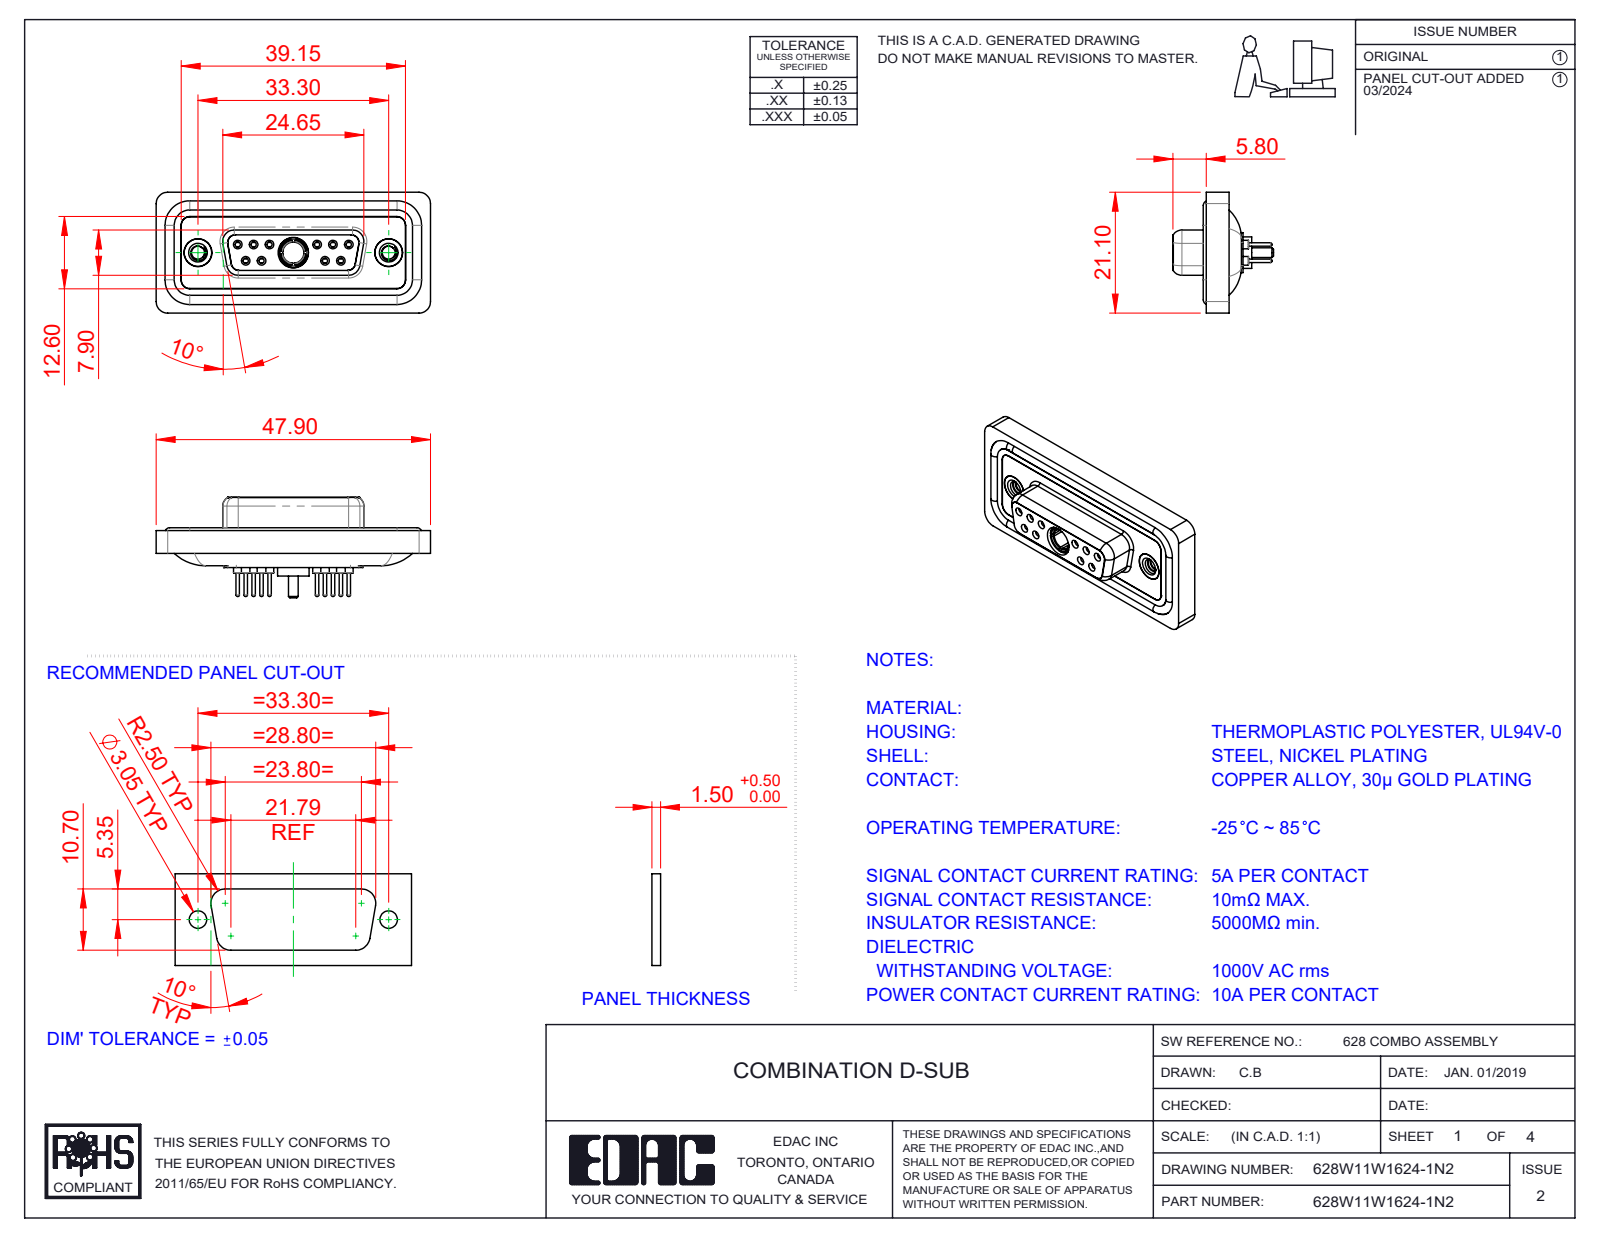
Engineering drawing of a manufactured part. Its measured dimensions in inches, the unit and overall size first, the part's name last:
Units: inches
Overall size (bounding box): 1.886 × 0.831 × 0.691
Round holes (diameter × count): ⌀0.035 ×10, ⌀0.043 ×10, ⌀0.059 ×10, ⌀0.079 ×10, ⌀0.067 ×6, ⌀0.063 ×4, ⌀0.191 ×3, ⌀0.089 ×2, ⌀0.157 ×2, ⌀0.159 ×2, ⌀0.197 ×2, ⌀0.146 ×1
Round bosses / shafts (diameter × count): ⌀0.087 ×10, ⌀0.063 ×10, ⌀0.024 ×10, ⌀0.195 ×2, ⌀0.189 ×2, ⌀0.217 ×1, ⌀0.205 ×1, ⌀0.195 ×1
Partial cylindrical surfaces — rounded edges, fillets, slot ends (radius × count): R0.059 ×22, R0.079 ×20, R0.053 ×12, R0.063 ×8, R0.01 ×4, R0.02 ×4, R0.024 ×4, R0.026 ×4
Main face-to-face distances: 0.016, 0.063, 0.071, 0.114, 0.02, 0.043, 0.222, 0.293, 0.26, 0.278
Hole centre spacings: 0.124, 0.109, 0.545, 0.436, 0.654, 0.198, 0.198, 0.218
Volume: 0.373 in³ · Surface area: 15.53 in²
Bodies: 19 solids, 1010 faces (284 planar, 401 cylindrical, 325 other)
Part name (STEP PRODUCT): 628Combo Housing_11W1; 628Combo Contact Row 2_24; 628Combo Waterproof Housing_15 Contacts; Power Socket_10A S (+5 more)
STEP written by: SolidWorks 2023 (CONFIG_CONTROL_DESIGN)
